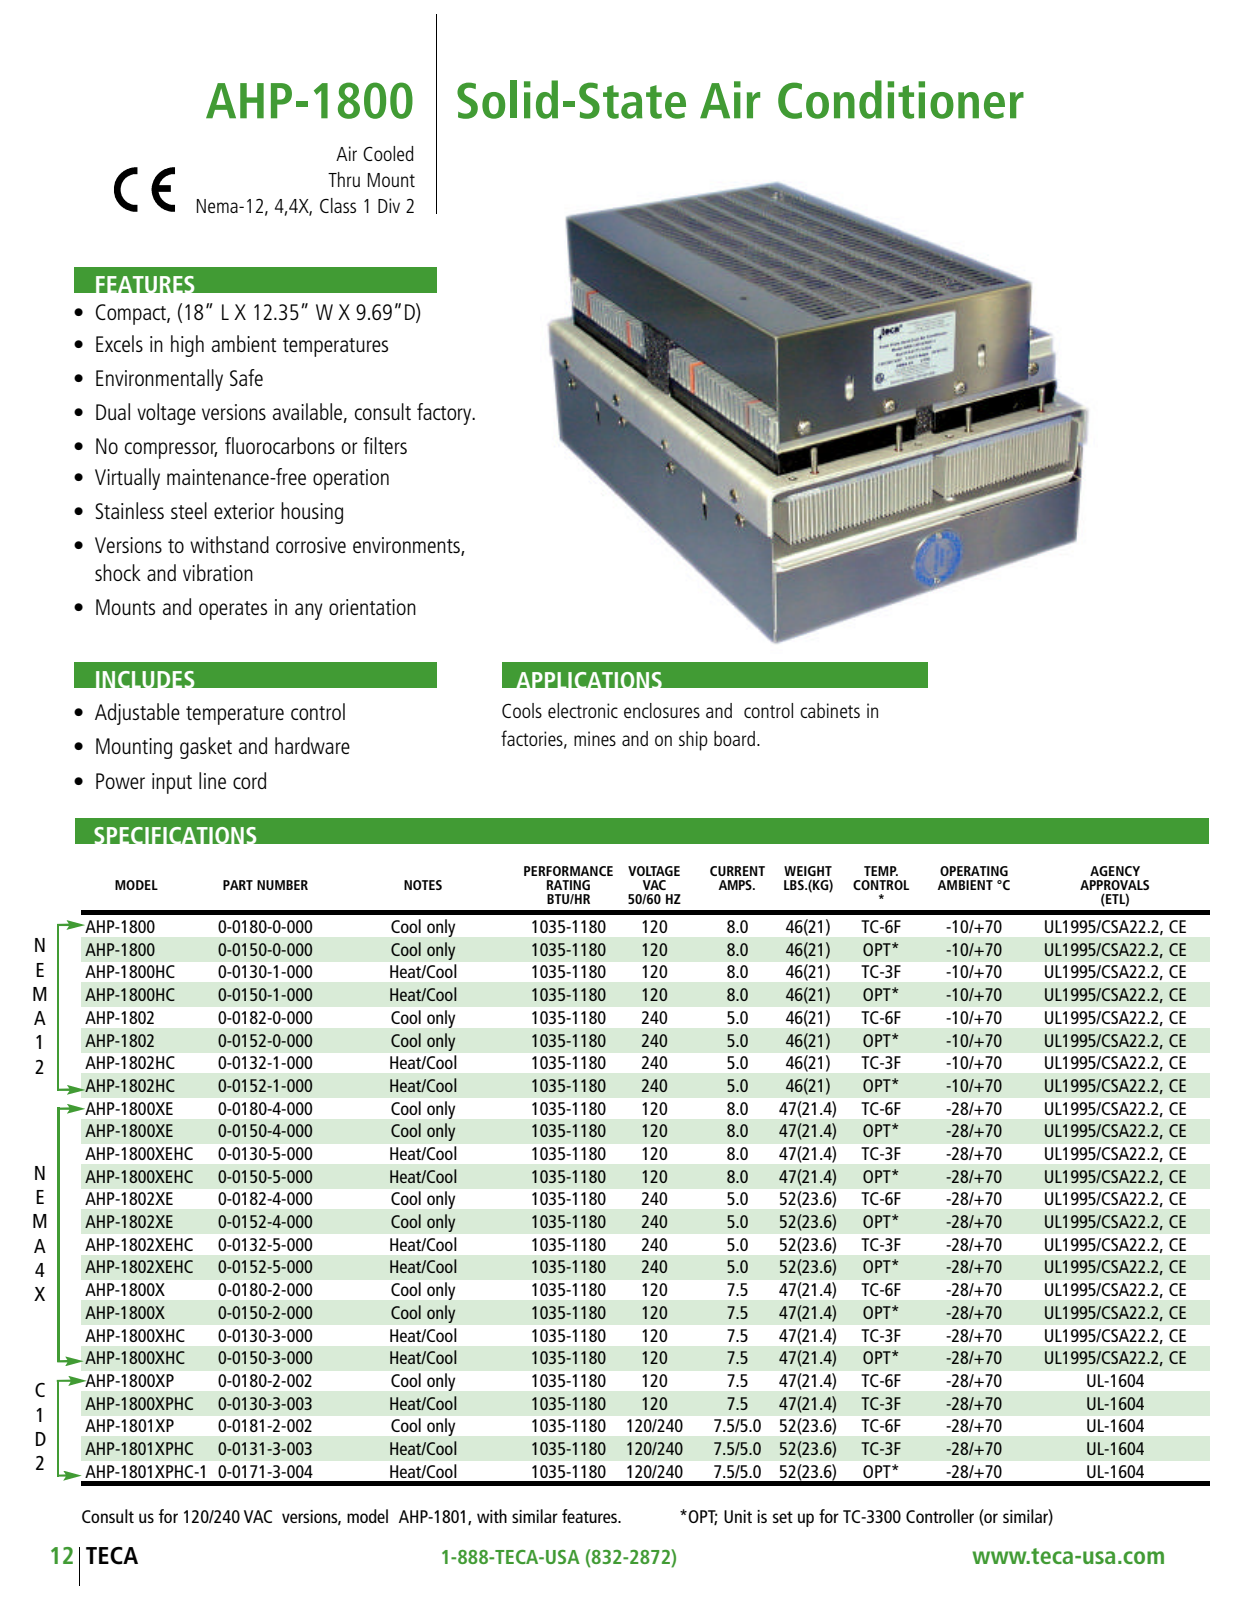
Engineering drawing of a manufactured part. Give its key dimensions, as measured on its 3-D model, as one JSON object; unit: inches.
{"part_name": "ahp-1800", "step_written_by": "SolidWorks 2016 (CONFIG_CONTROL_DESIGN)", "units": "inches", "bodies": {"solids": 79, "faces": 4653, "planar": 4519, "cylindrical": 130, "other": 4}, "overall_size": [18, 14.56, 9.85], "volume_in3": 562.8, "surface_area_in2": 8480, "round_holes": [[0.188, 8], [4.5, 2], [5.75, 2], [0.365, 1], [0.4, 1], [0.75, 1]], "round_bosses_or_shafts": [[3, 3], [2.25, 1], [1, 1], [0.527, 1], [0.414, 1], [0.38, 1], [0.25, 1], [0.15, 1]], "partial_cylinders_radius": [[4.072, 12], [4.74, 12], [3.054, 4], [3.555, 4], [2.8, 3], [3.25, 2], [3.375, 2], [0.75, 1]], "face_to_face_distances": [0.09, 2.72, 0.15, 7.43, 4.71, 0.3, 0.45, 9.6, 6.88, 2.17], "hole_center_spacings": [3, 5.68, 8.733, 8.788, 9.66, 11.329, 17.26, 17.519]}
